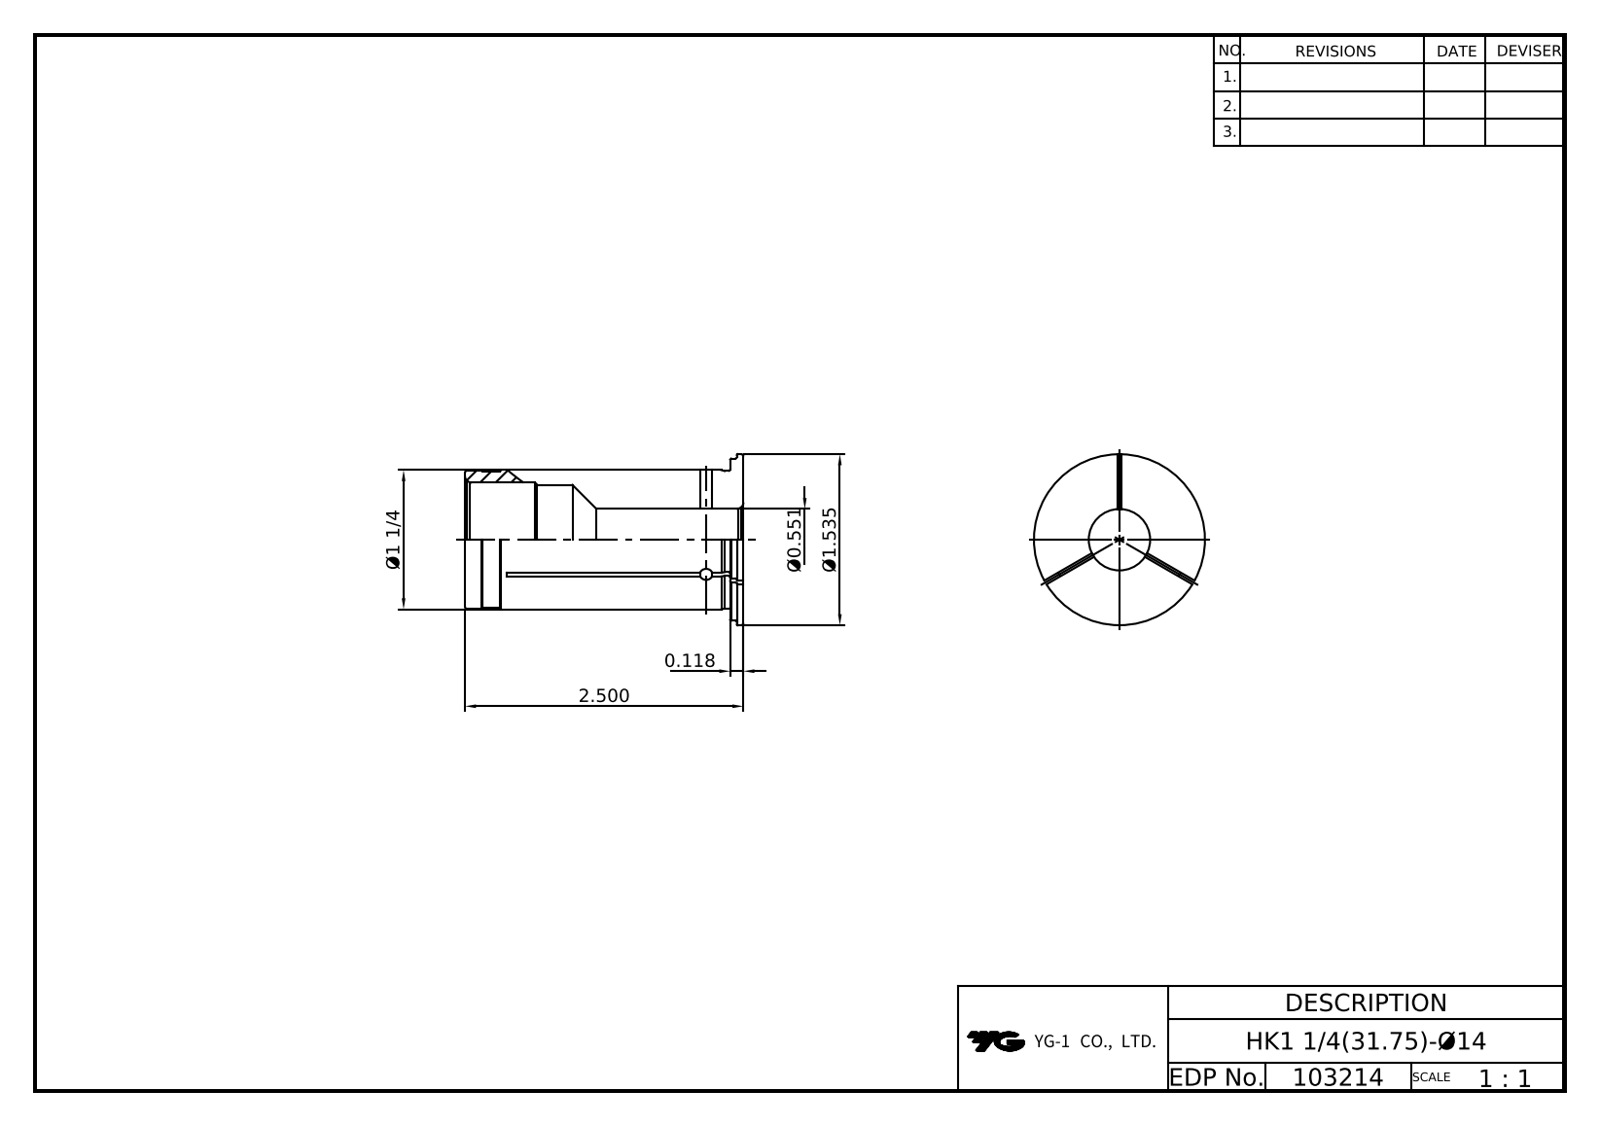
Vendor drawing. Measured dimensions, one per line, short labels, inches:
name: LO-HK31.75-14
written by: Autodesk Inventor 2025 (AP242_MANAGED_MODEL_BASED_3D_ENGINEERING_MIM_LF)
unit: in
bodies: 1 solid, 16 faces (4 planar, 6 cylindrical, 6 other)
size: 2.5 × 1.535 × 1.535
volume: 1.939 in³; area: 18.55 in²
holes: 1× ⌀0.551, 1× ⌀0.984, 1× ⌀1.024
bosses: 1× ⌀1.535, 1× ⌀1.457, 1× ⌀1.25
face distances: 2.5, 2.382, 0.118, 0.059, 2.441
